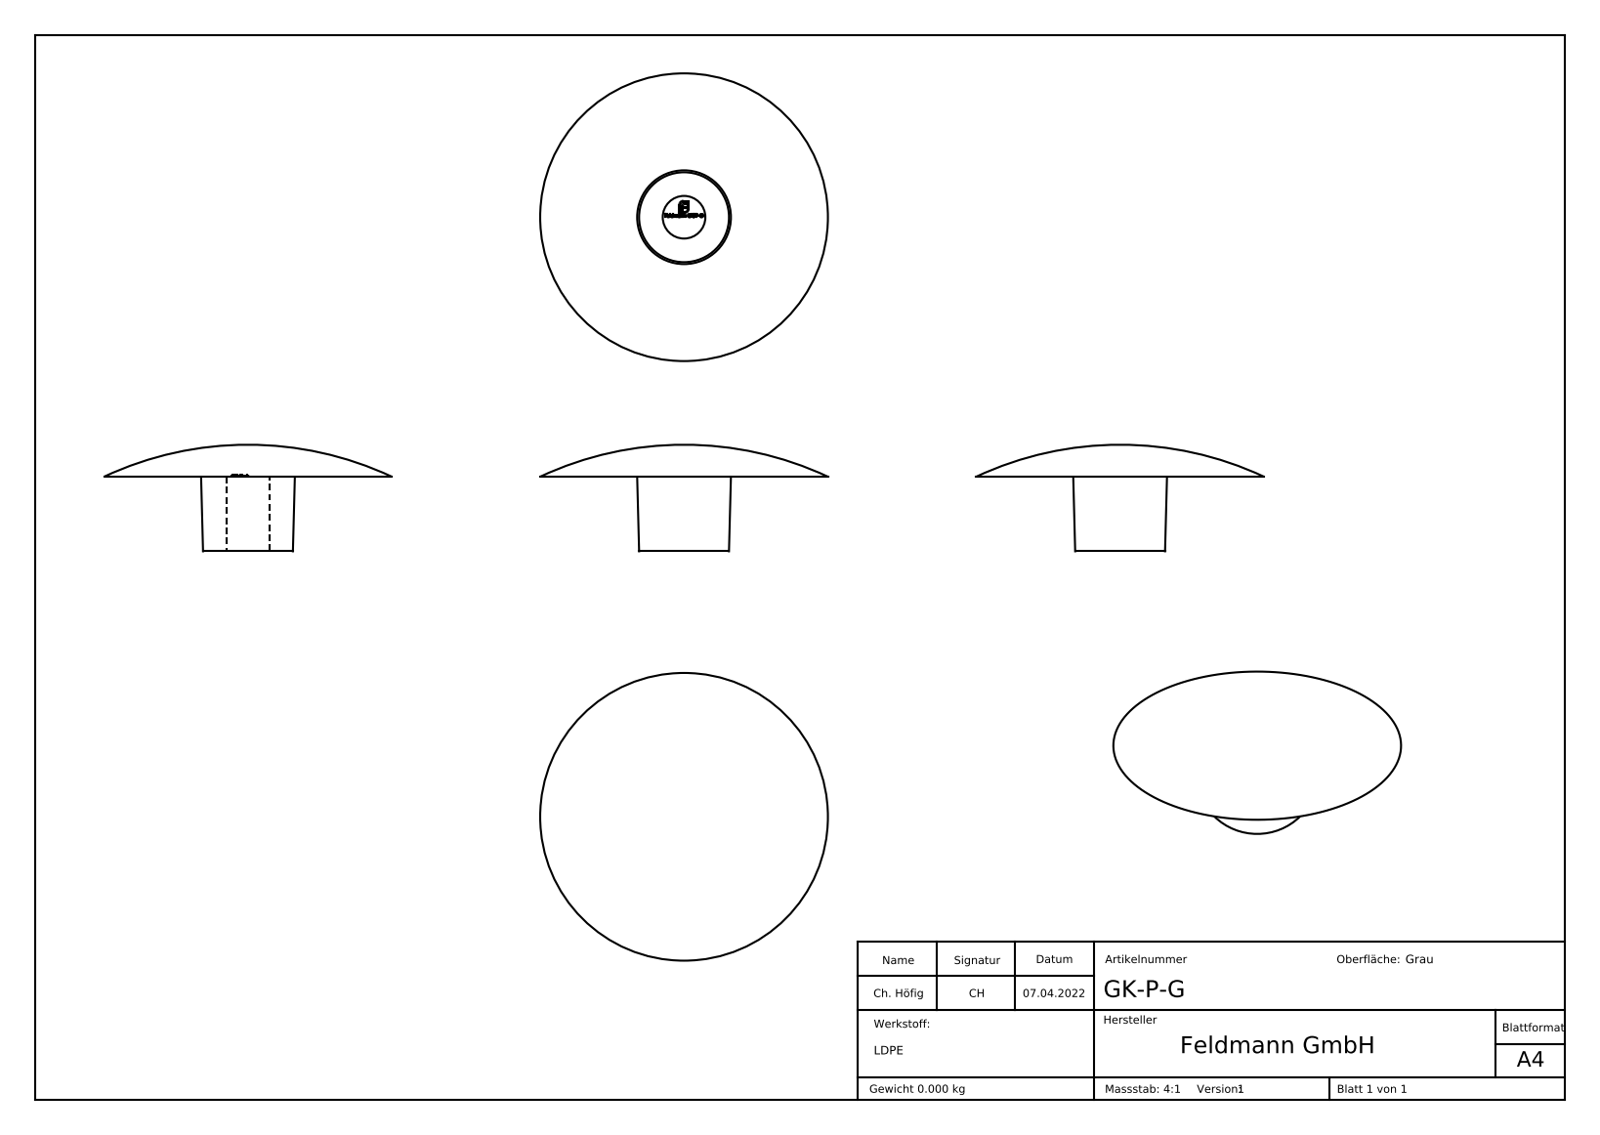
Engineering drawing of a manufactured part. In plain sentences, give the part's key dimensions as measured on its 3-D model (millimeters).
The part is named "GK-P-G". Its 3-D file was written by "SolidWorks 2018 (CONFIG_CONTROL_DESIGN)". It is 1 solid with 228 faces: 133 planar, 1 cylindrical and 94 other. Overall it measures 13.5 by 13.5 by 5 millimeters. Its volume is 149 cubic millimeters and its surface area 363 square millimeters. Round holes: 1 of diameter 2. The main face-to-face distances are 3.5, 3.6, 0.4, 0.34, 0.42, 0.35, 0.53, 0.36, 0.72, 0.38.
